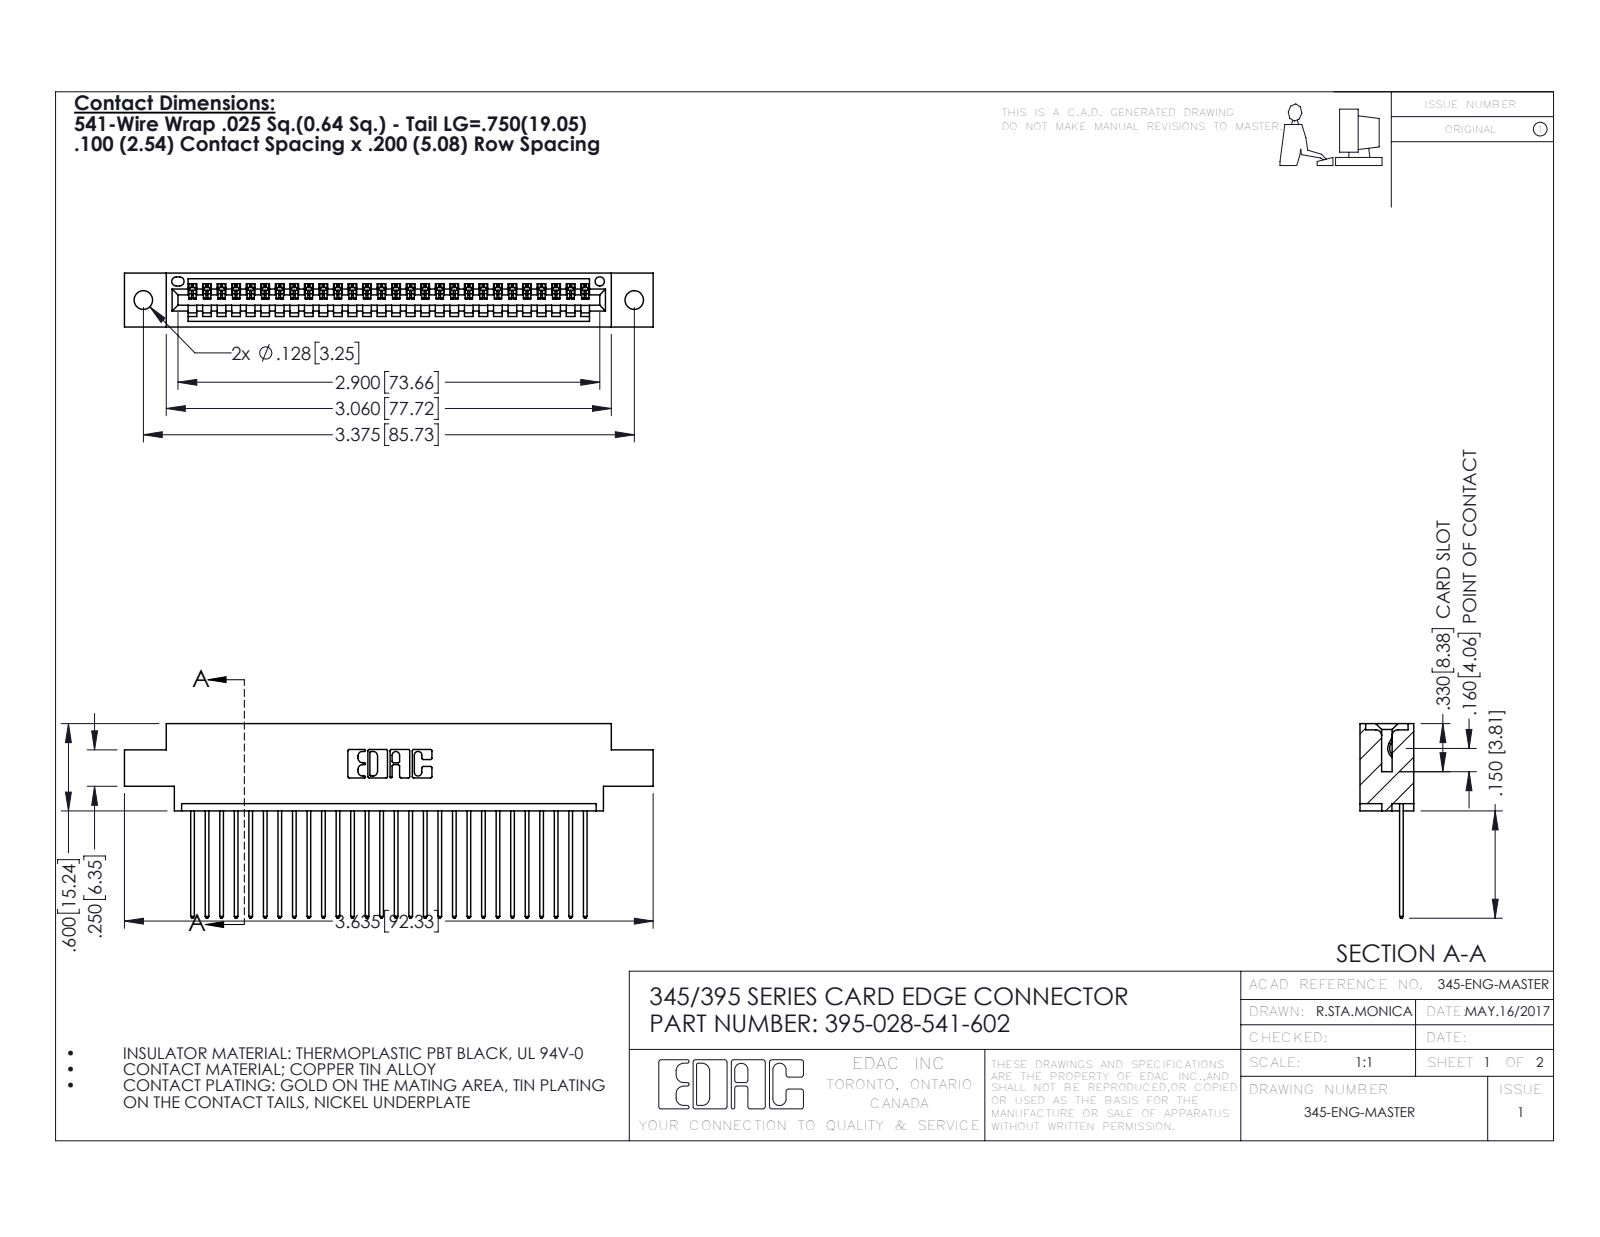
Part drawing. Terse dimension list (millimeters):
name: 395-028-541-602; 345 Part_0.170 Offset - 0.128 Dia; 345-292-001_345-293-141
written by: SolidWorks 2016 (CONFIG_CONTROL_DESIGN)
unit: mm
bodies: 29 solids, 1754 faces (1204 planar, 550 cylindrical, 0 other)
size: 92.3 × 34 × 9.4
volume: 8 600 mm³; area: 11 630 mm²
holes: 2× ⌀3.3, 1× ⌀1.6
rounds: 56× R0.2, 56× R0.3, 22× R0.3, 6× R0.2, 6× R0.8, 3× R0.7, 2× R0.8, 2× R1
face distances: 1.8, 7.6, 9.4, 2.5, 6.9, 0.6, 5.1, 5.7, 4.4, 3.8
hole spacings: 6.9, 79.8, 85.7
